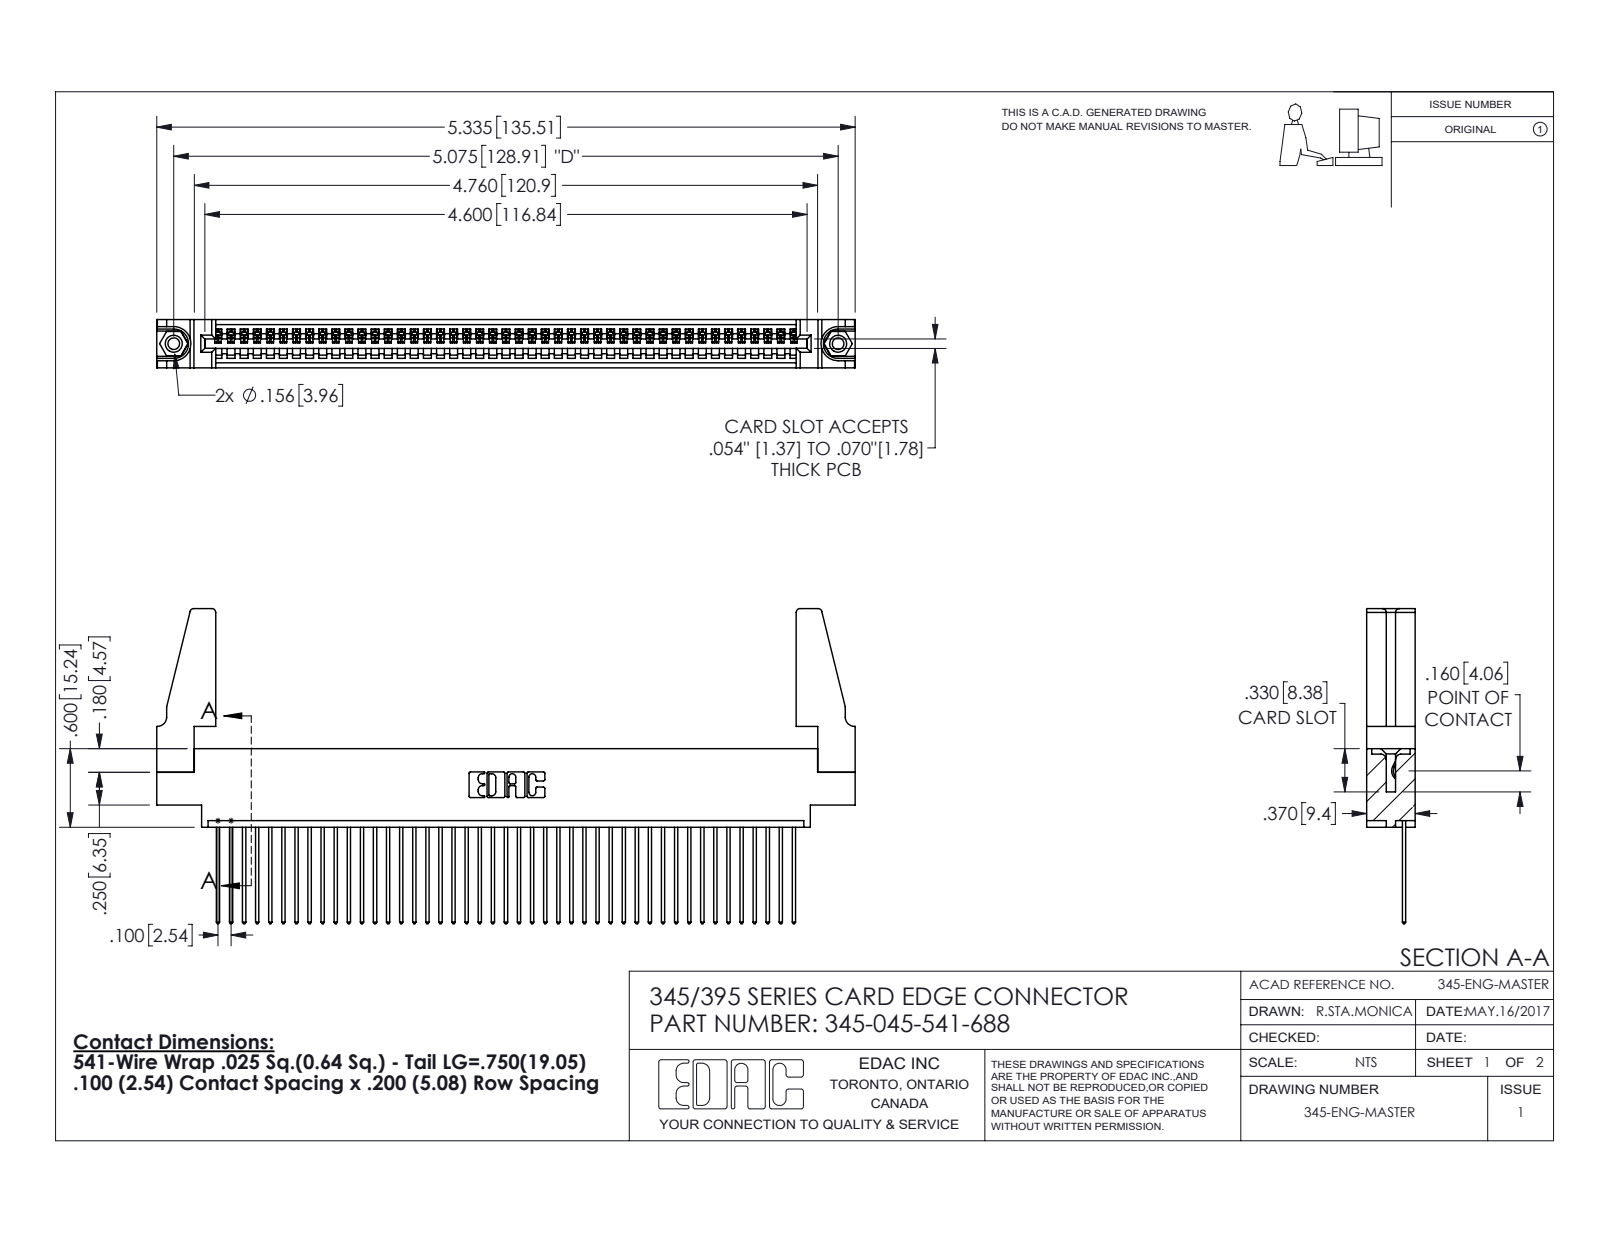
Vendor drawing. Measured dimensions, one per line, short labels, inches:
name: 345-220-078_345-220-088; 345-292-001_345-293-141; 345-250-001_345-250-001-102; 345-045-541-688 (+1 more)
written by: SolidWorks 2016 (CONFIG_CONTROL_DESIGN)
unit: in
bodies: 50 solids, 2864 faces (1956 planar, 892 cylindrical, 16 other)
size: 5.336 × 2.407 × 0.37
volume: 0.988 in³; area: 33.1 in²
holes: 2× ⌀0.089, 2× ⌀0.125, 2× ⌀0.156, 1× ⌀0.064
bosses: 2× ⌀0.155
rounds: 90× R0.006, 90× R0.01, 22× R0.01, 8× R0.03, 6× R0.007, 6× R0.031, 3× R0.026, 2× R0.031
face distances: 0.072, 0.298, 0.37, 0.098, 0.272, 0.025, 0.2, 0.225, 0.175, 0.149
hole spacings: 0.27, 4.839, 5.075
